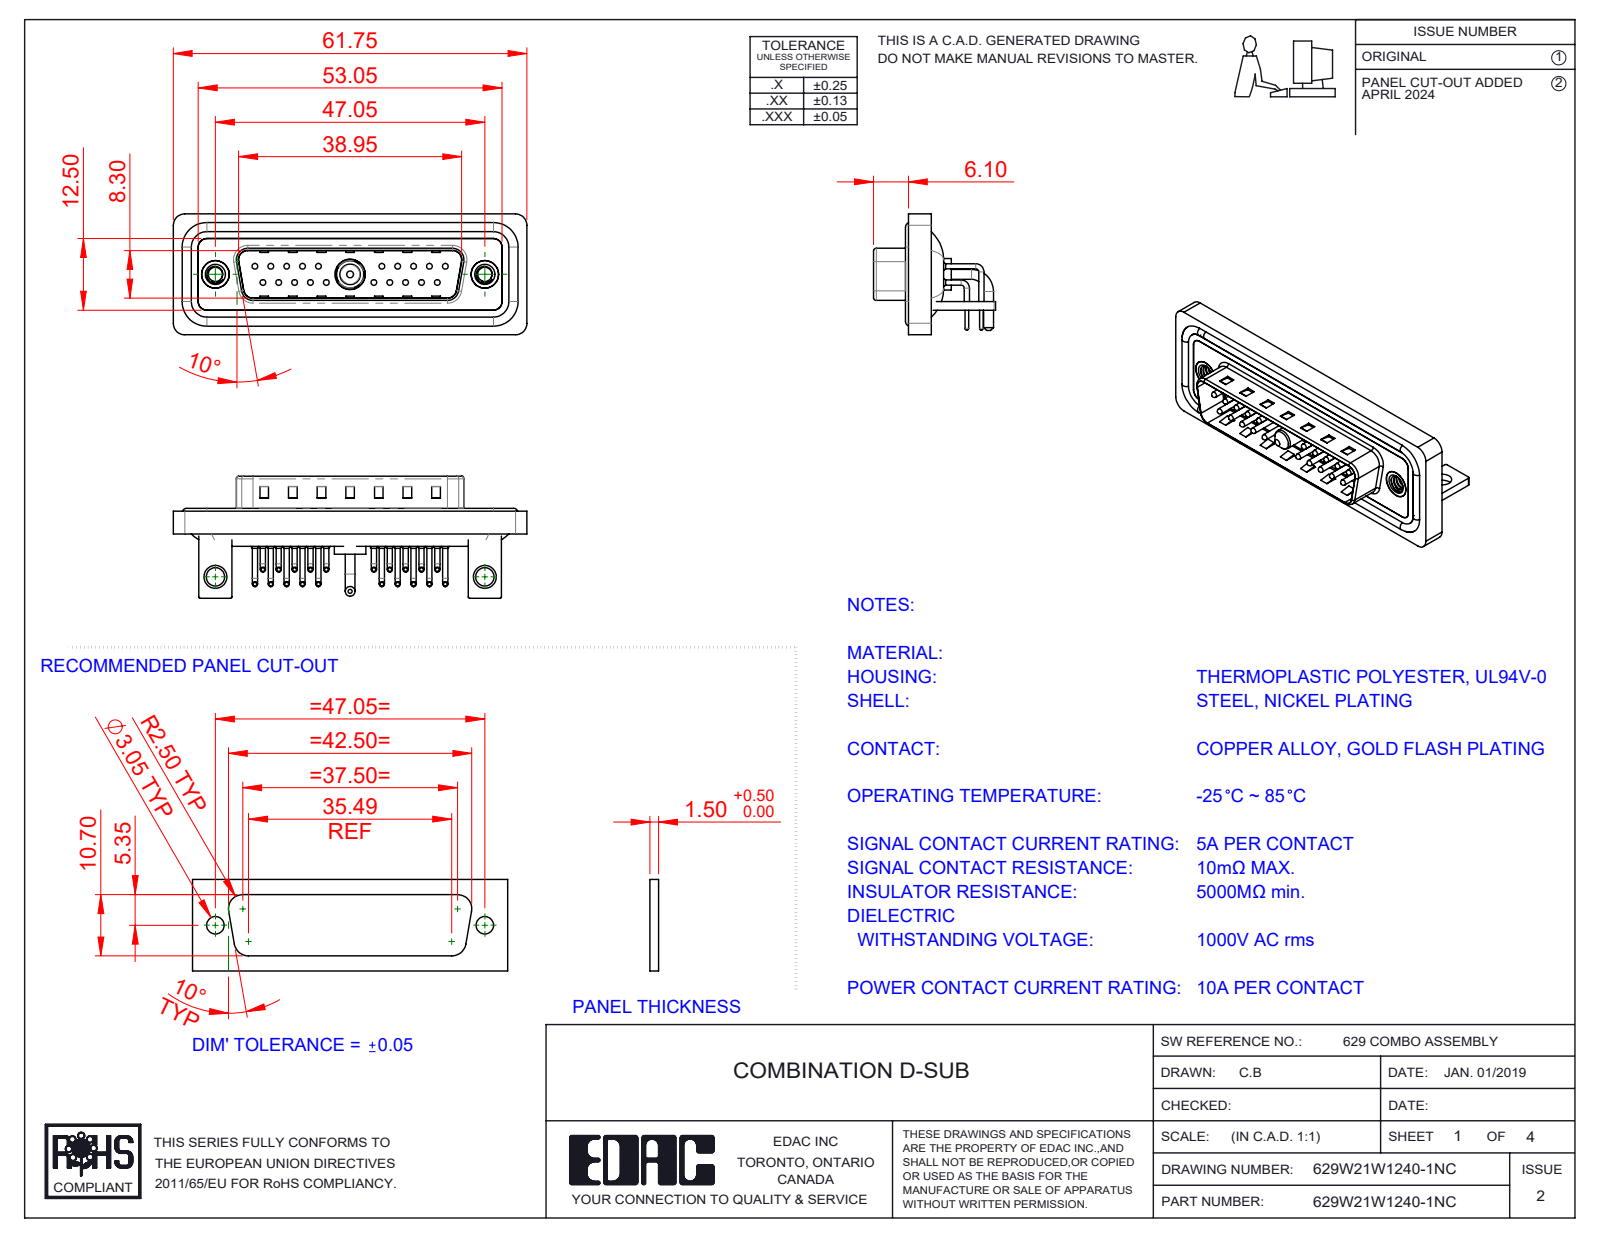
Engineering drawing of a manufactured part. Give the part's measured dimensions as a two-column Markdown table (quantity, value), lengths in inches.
| quantity | value |
| --- | --- |
| part name | 629Combo Shell Rear_25 Contacts; Power Pin_10A RA; 629Combo Threaded Rivet_B; 629W21W1240-1NC (+6 more) |
| STEP written by | SolidWorks 2023 (CONFIG_CONTROL_DESIGN) |
| units | inches |
| bodies | 31 solids, 2764 faces (1519 planar, 947 cylindrical, 298 other) |
| overall size | 2.431 × 0.839 × 0.831 |
| volume | 0.466 in³ |
| surface area | 20.55 in² |
| round holes (diameter × count) | 0.03 × 20, 0.063 × 20, 0.079 × 20, 0.098 × 2, 0.126 × 2, 0.157 × 2, 0.189 × 2, 0.197 × 2, 0.191 × 1, 0.209 × 1 |
| round bosses / shafts (diameter × count) | 0.035 × 40, 0.059 × 20, 0.039 × 20, 0.026 × 20, 0.063 × 4, 0.193 × 2, 0.067 × 2, 0.217 × 1 |
| partial cylindrical surfaces (radius × count) | 0.04 × 20, 0.079 × 19, 0.059 × 18, 0.01 × 16, 0.02 × 9, 0.063 × 8, 0.024 × 4, 0.026 × 4 |
| main face-to-face distances | 0.016, 0.031, 0.083, 0.114, 0.059, 0.043, 0.161, 0.063, 0.177, 0.146 |
| hole center spacings | 0.124, 0.109, 0.218, 0.327, 0.198, 0.763, 0.826, 0.872 |
